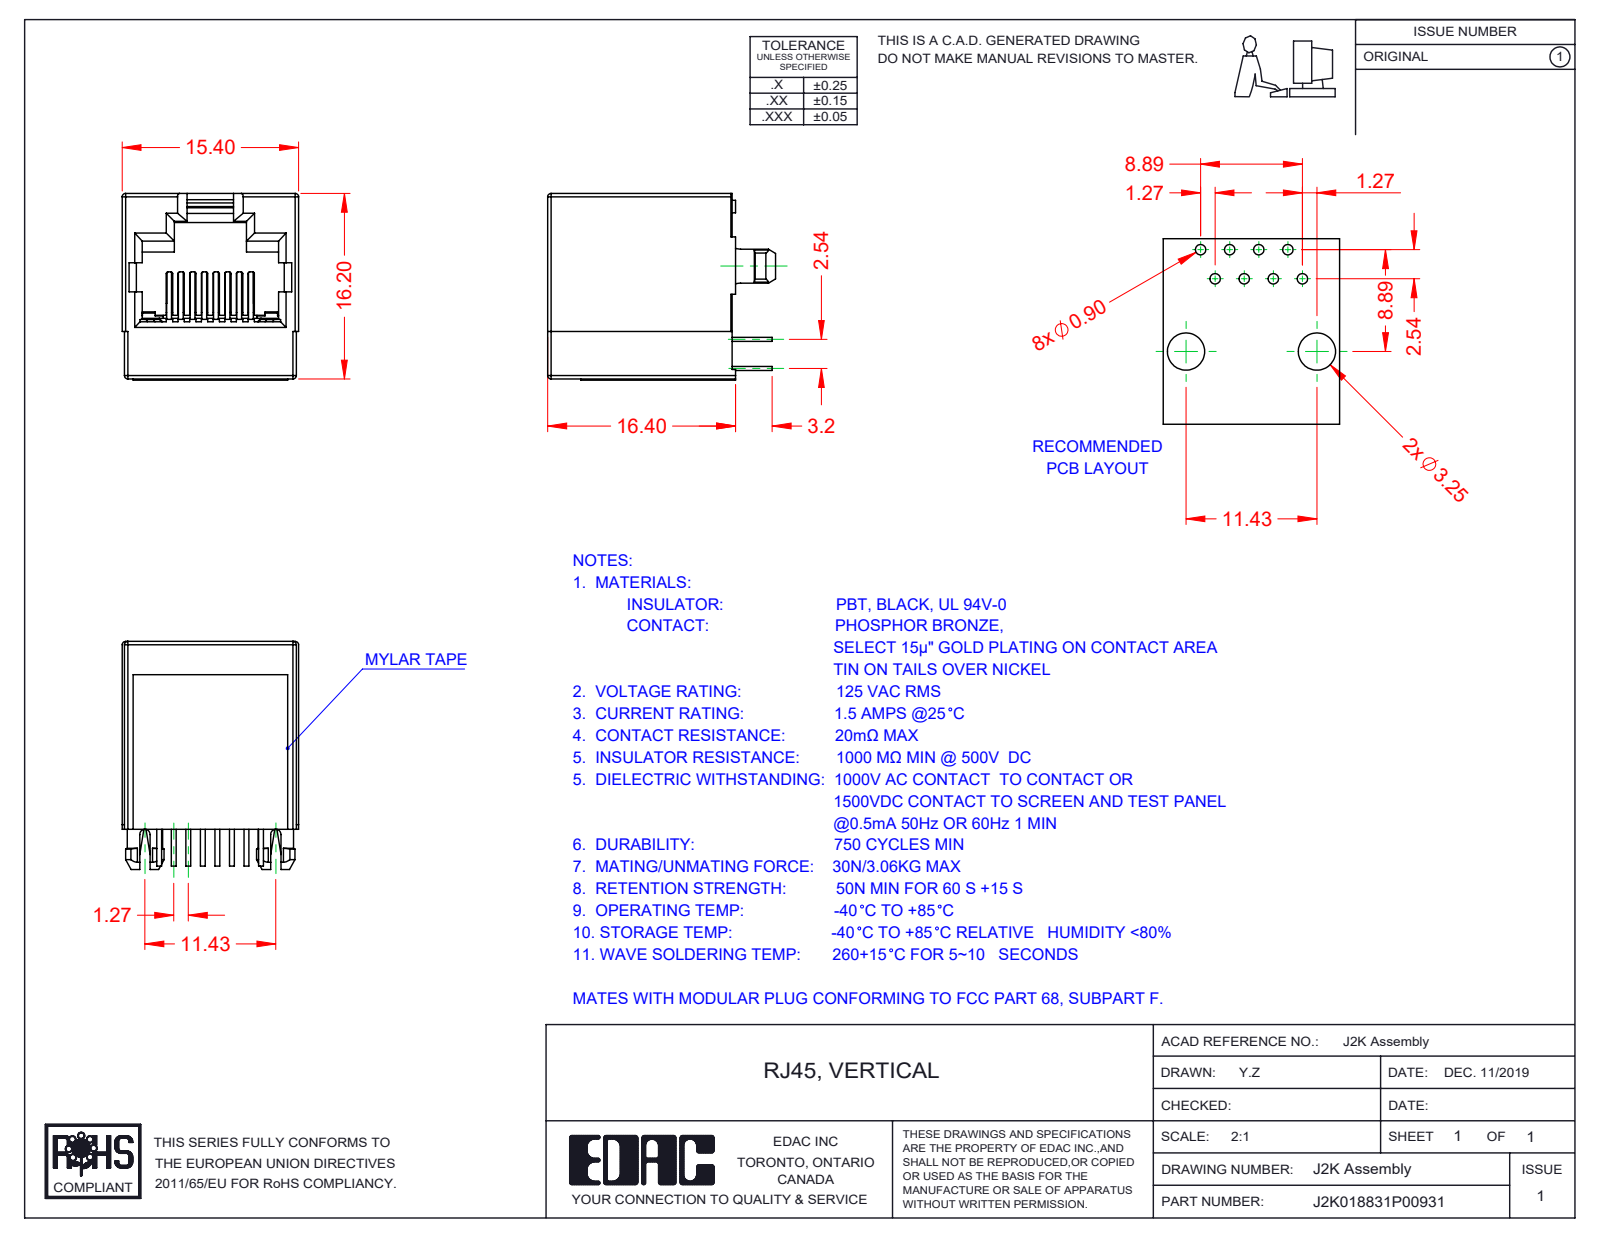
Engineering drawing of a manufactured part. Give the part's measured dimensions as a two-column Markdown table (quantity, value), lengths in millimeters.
| quantity | value |
| --- | --- |
| part name | 2K Insulator; RJ2K018831P00931; 2K Contact Lock; 2K Mylar Tape (+1 more) |
| STEP written by | SolidWorks 2016 (CONFIG_CONTROL_DESIGN) |
| units | millimeters |
| bodies | 11 solids, 729 faces (592 planar, 113 cylindrical, 24 other) |
| overall size | 19.9 × 16.3 × 15.4 |
| volume | 2 491 mm³ |
| surface area | 4 332 mm² |
| round bosses / shafts (diameter × count) | 3.1 × 2, 1.1 × 2 |
| partial cylindrical surfaces (radius × count) | 0.15 × 16, 0.3 × 10, 0.5 × 3, 0.1 × 2, 0.2 × 2, 0.45 × 2, 0.6 × 2, 0.95 × 2 |
| main face-to-face distances | 16.2, 15.4, 16.3, 14, 1.4, 1.2, 13.8, 15.2, 0.5, 1.3 |
